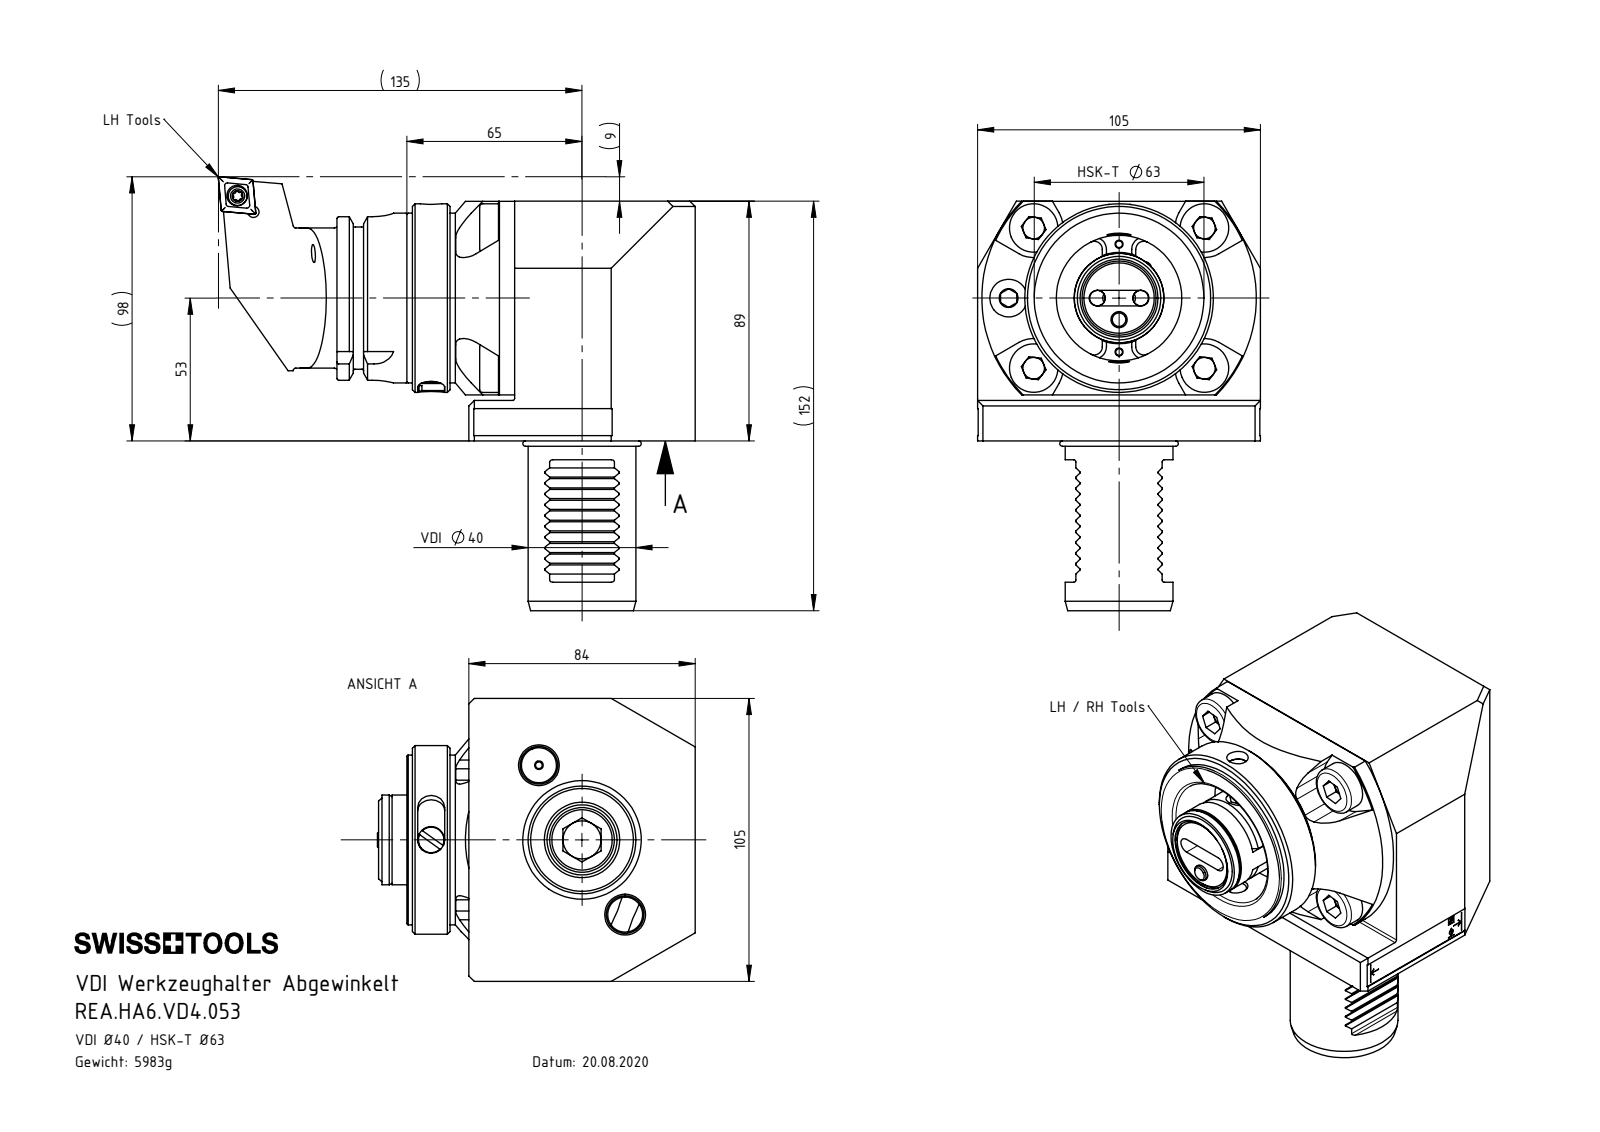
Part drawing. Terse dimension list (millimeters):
name: HA6-ER2.002.010; ISO 4762 - M16 x 65; REA-HA6.VD4.053-11_A; VD4-ER1.014.010_A (+8 more)
written by: SolidWorks 2022 (AUTOMOTIVE_DESIGN)
unit: mm
bodies: 26 solids, 875 faces (360 planar, 267 cylindrical, 248 other)
size: 152 × 117.95 × 105
volume: 779 880 mm³; area: 151 706 mm²
holes: 6× ⌀13, 4× ⌀6.8, 4× ⌀10.2, 3× ⌀2.5, 3× ⌀4, 3× ⌀8.5, 3× ⌀14, 2× ⌀5, 2× ⌀5.75, 2× ⌀5.8, 2× ⌀8, 1× ⌀6
bosses: 4× ⌀18, 4× ⌀12, 2× ⌀16, 2× ⌀8, 1× ⌀70, 1× ⌀63, 1× ⌀62.5, 1× ⌀58.75
rounds: 20× R0.3, 12× R3, 8× R5, 5× R0.8, 5× R11, 4× R2.9, 2× R1, 2× R2.88
face distances: 67, 89, 20, 22.5, 44.5, 47, 2.5, 105, 11, 34
hole spacings: 41, 21.54, 32.26, 35.18, 47.46, 55.86, 8, 11.31
